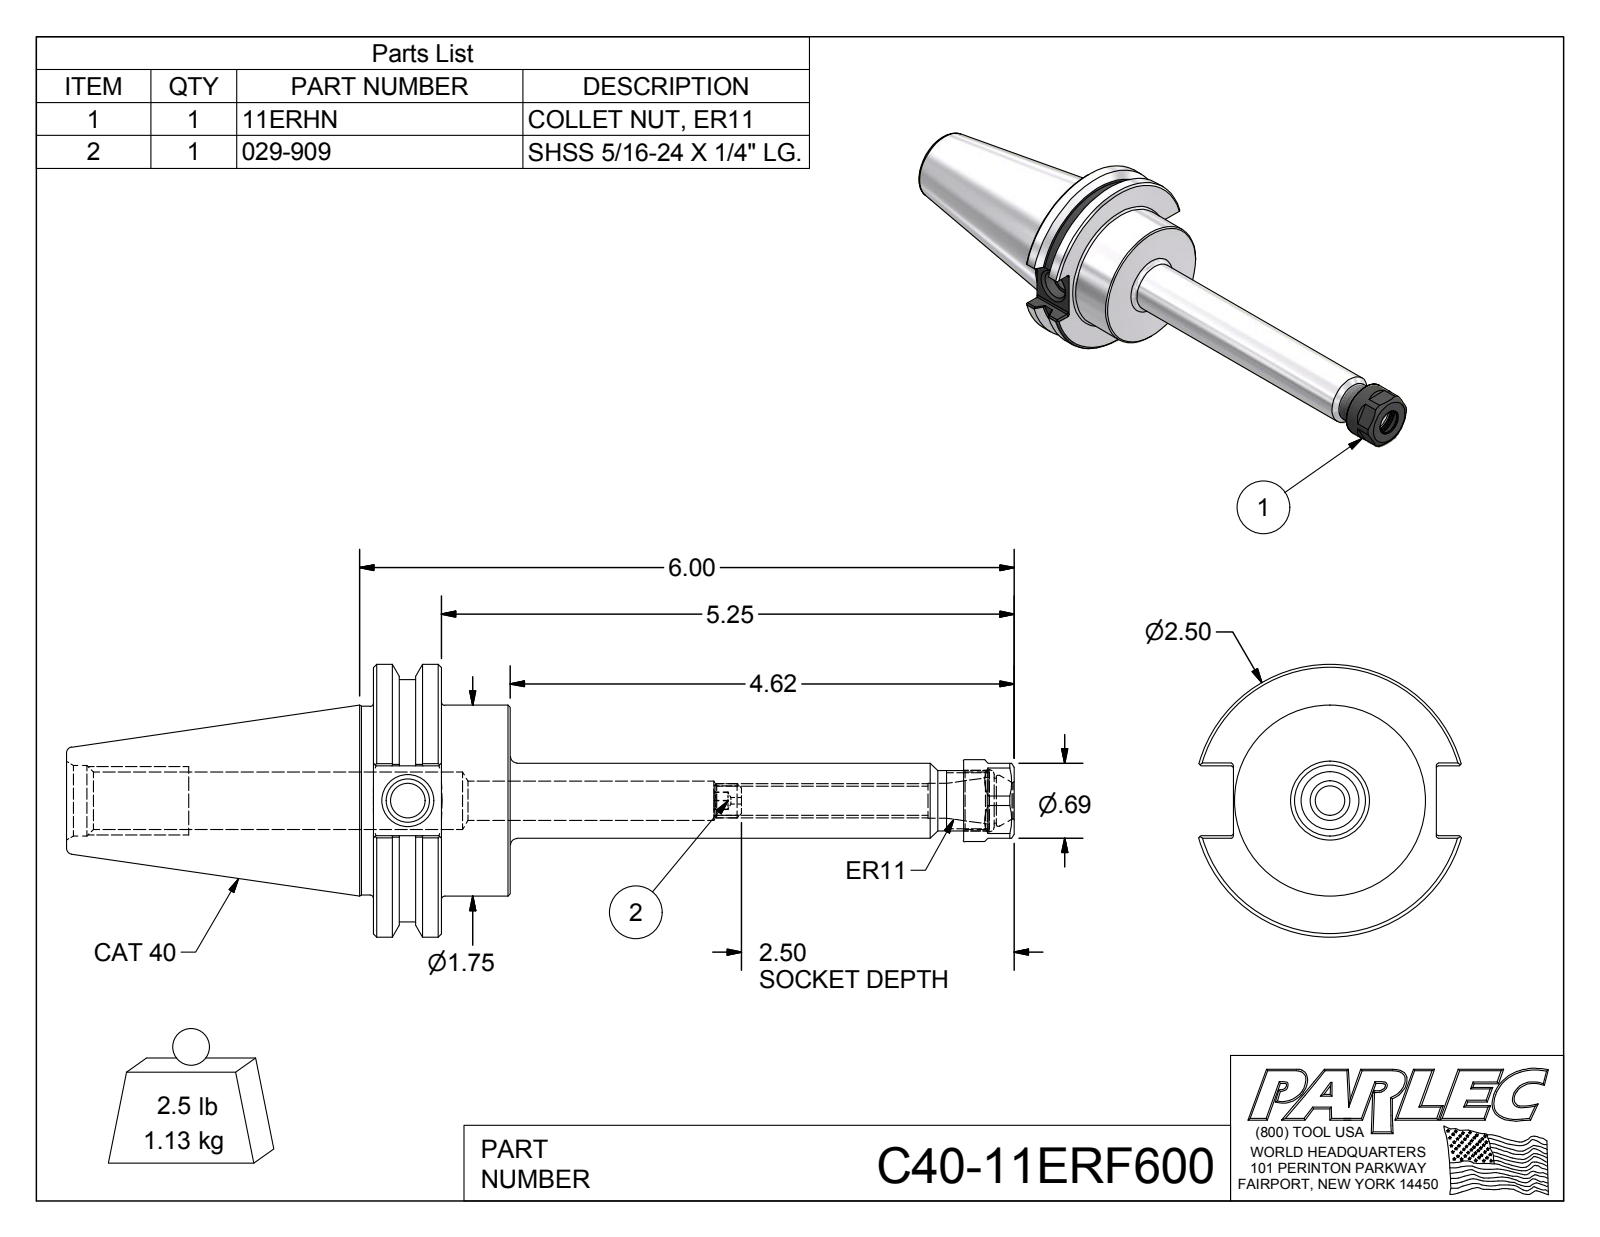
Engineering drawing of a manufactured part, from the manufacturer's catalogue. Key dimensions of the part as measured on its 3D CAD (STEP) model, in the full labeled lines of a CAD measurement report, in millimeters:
Part name (STEP PRODUCT): C40-11ERF600; C40-11ER6-1; 11ERHN; 029-909
STEP written by: Autodesk Inventor 2012 (AUTOMOTIVE_DESIGN)
Units: millimetres
Bodies: 3 solids, 151 faces (64 planar, 36 cylindrical, 51 other)
Overall size (bounding box): 220.6 × 63.5 × 61.1
Volume: 145 500 mm³ · Surface area: 33 550 mm²
Round holes (diameter × count): ⌀1.5 ×1, ⌀6.8 ×1, ⌀8 ×1, ⌀8.1 ×1, ⌀8.5 ×1, ⌀9.1 ×1, ⌀10.1 ×1, ⌀11.8 ×1, ⌀13.3 ×1, ⌀13.4 ×1, ⌀14.4 ×1, ⌀16.5 ×1
Round bosses / shafts (diameter × count): ⌀63.5 ×1, ⌀56.4 ×1, ⌀44.5 ×1, ⌀43.9 ×1, ⌀19.1 ×1, ⌀17.5 ×1, ⌀14 ×1, ⌀8 ×1
Partial cylindrical surfaces — rounded edges, fillets, slot ends (radius × count): R0.5 ×12
Main face-to-face distances: 31.9, 15.9, 16, 16.3, 47.2, 149.2, 133.4, 117.3, 71.4, 87.3
